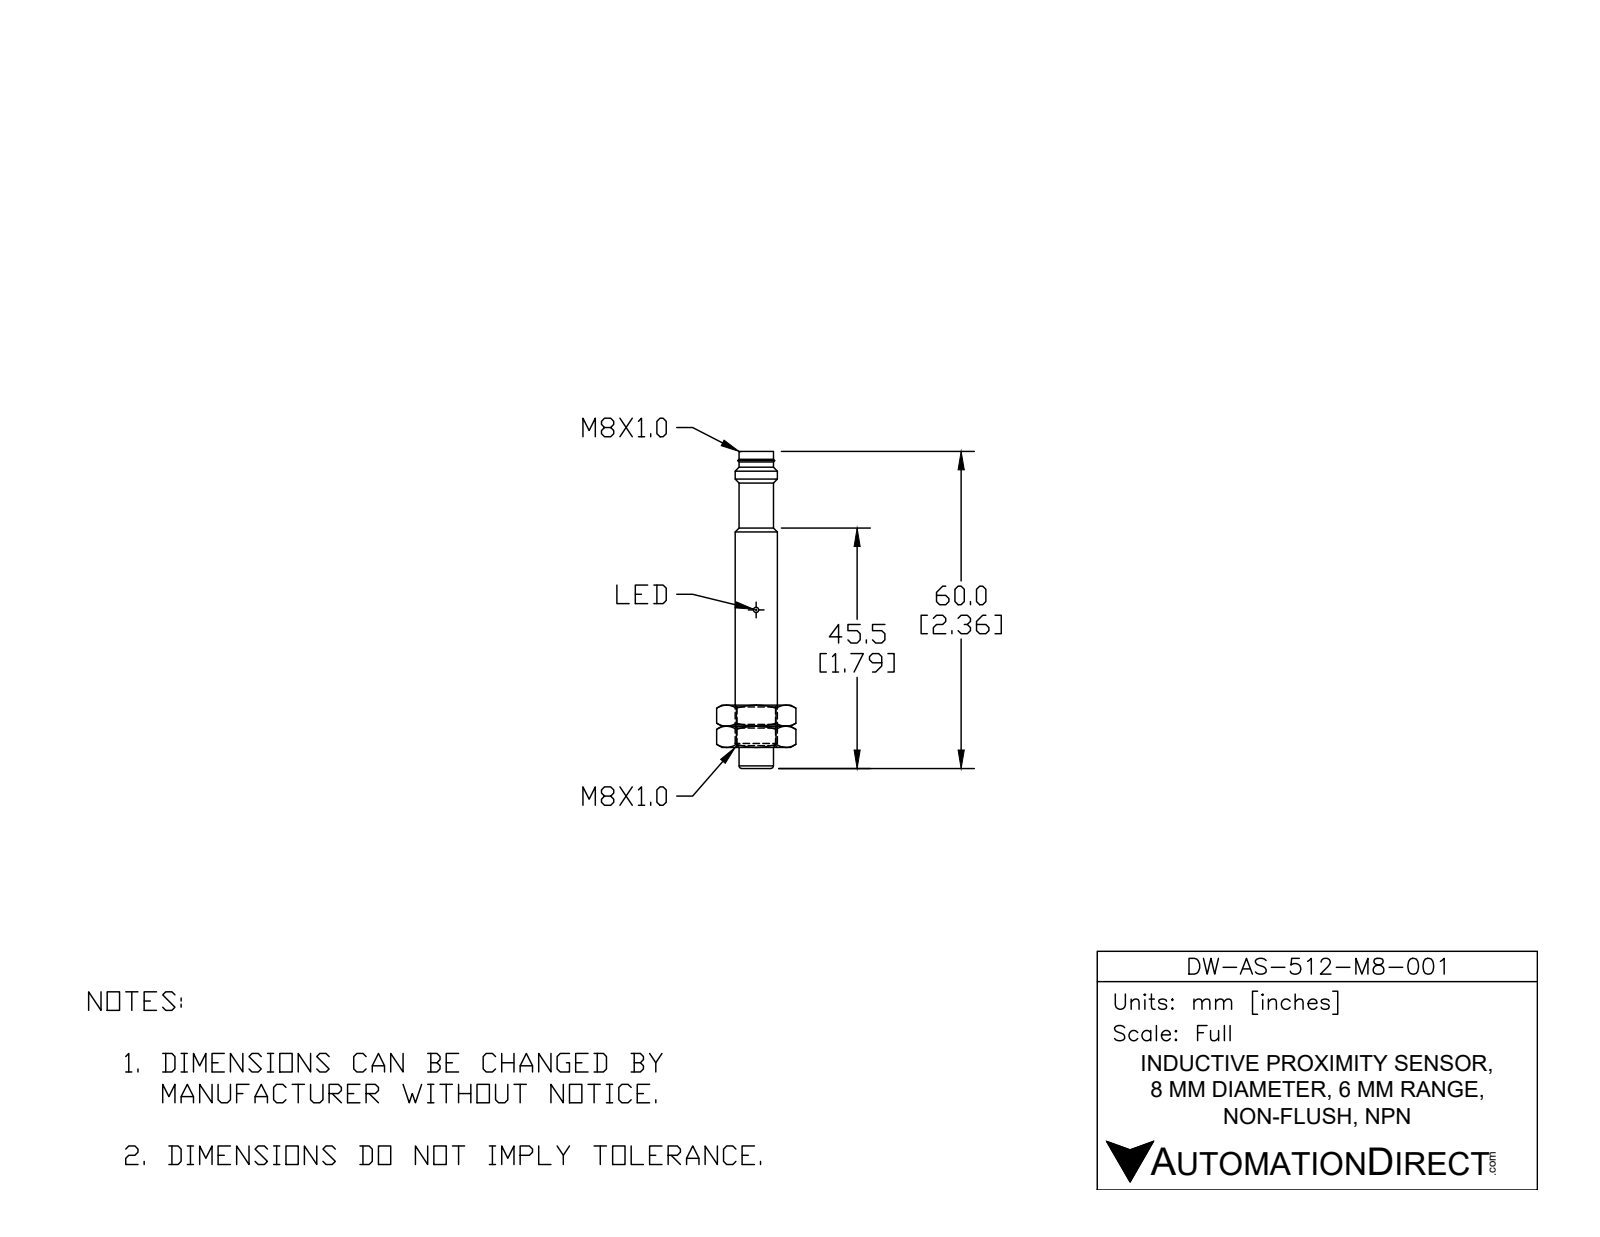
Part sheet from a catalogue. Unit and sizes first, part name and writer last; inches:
Units: inches
Overall size (bounding box): 2.362 × 0.315 × 0.315
Round holes (diameter × count): ⌀0.071 ×2
Round bosses / shafts (diameter × count): ⌀0.039 ×3, ⌀0.315 ×1, ⌀0.272 ×1, ⌀0.256 ×1, ⌀0.236 ×1
Main face-to-face distances: 2.165, 2.362, 0.197
Volume: 0.16 in³ · Surface area: 2.606 in²
Bodies: 1 solid, 33 faces (3 planar, 18 cylindrical, 12 other)
Part name (STEP PRODUCT): DW-AS-512-M8-001
STEP written by: SolidWorks 2017 (AUTOMOTIVE_DESIGN)
